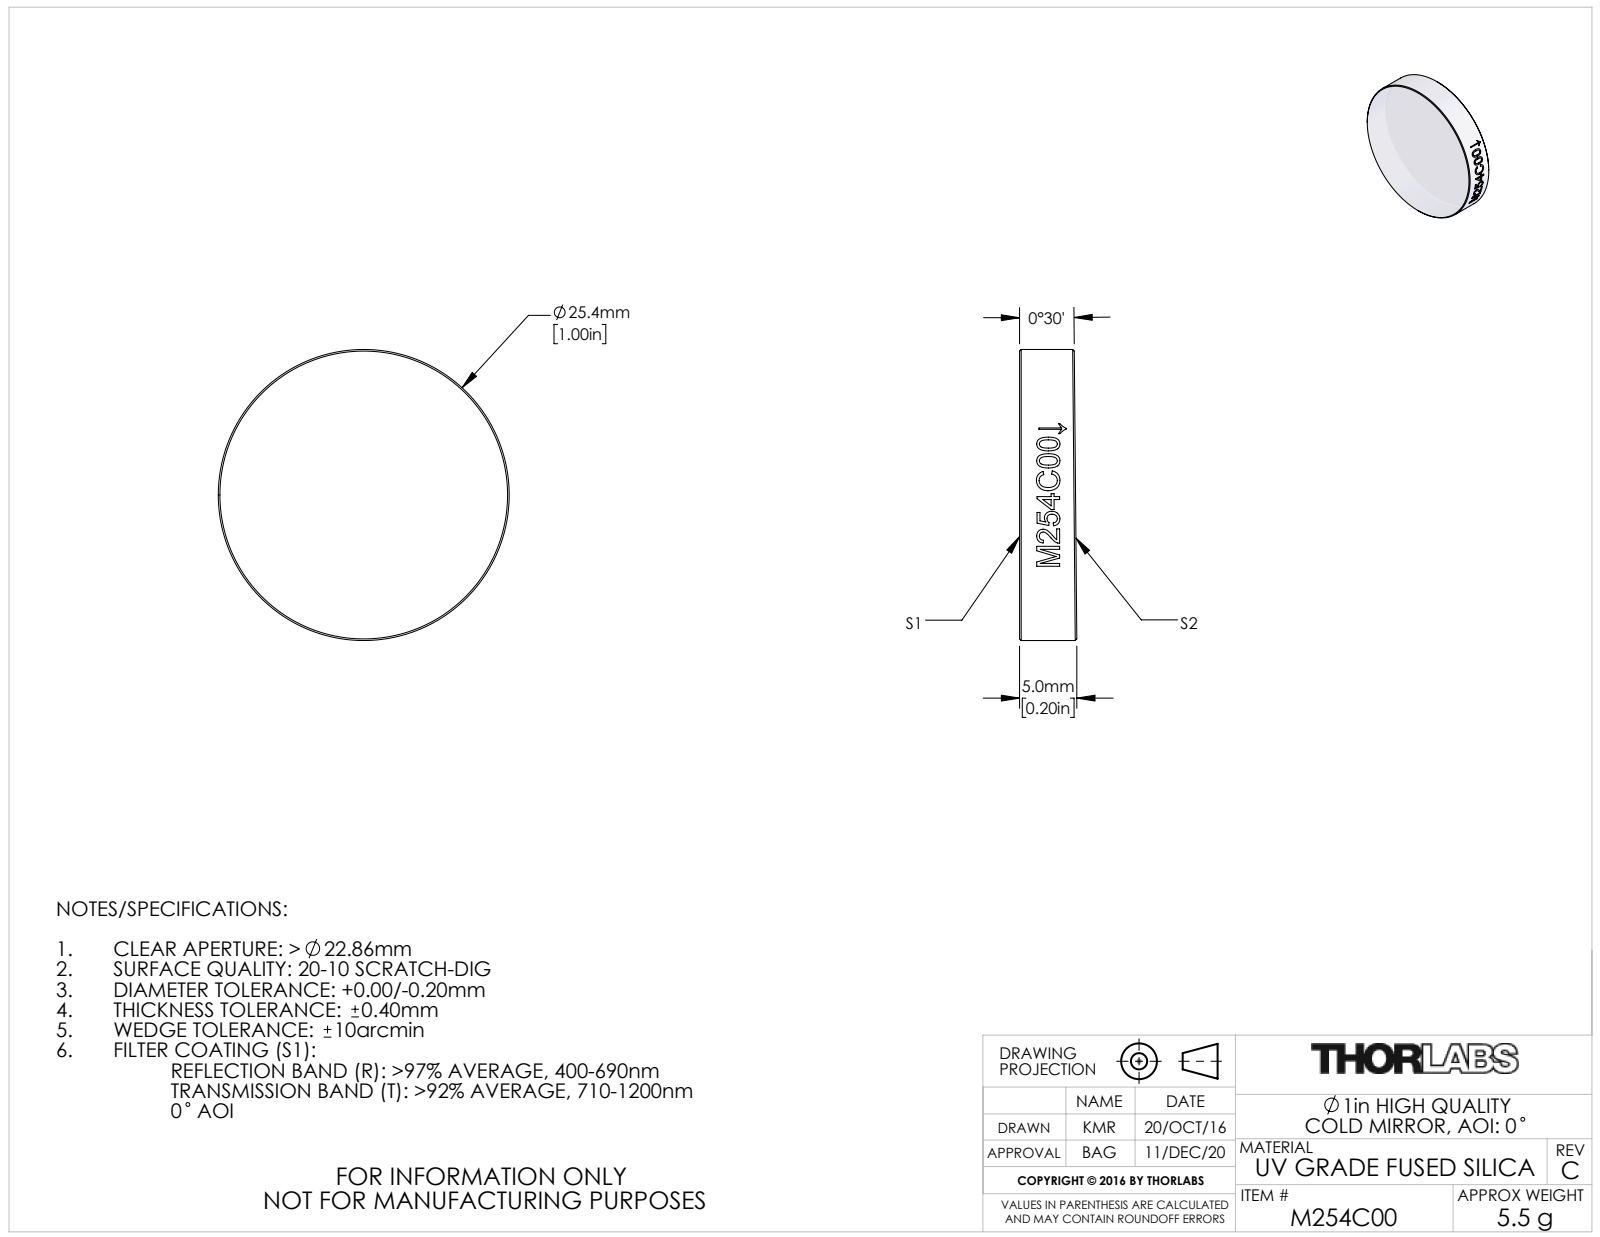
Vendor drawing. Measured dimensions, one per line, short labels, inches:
name: 23772-E0W
written by: SolidWorks 2016 (CONFIG_CONTROL_DESIGN)
unit: in
bodies: 1 solid, 20 faces (2 planar, 14 cylindrical, 4 other)
size: 1 × 1 × 0.197
volume: 0.151 in³; area: 2.155 in²
bosses: 1× ⌀1
